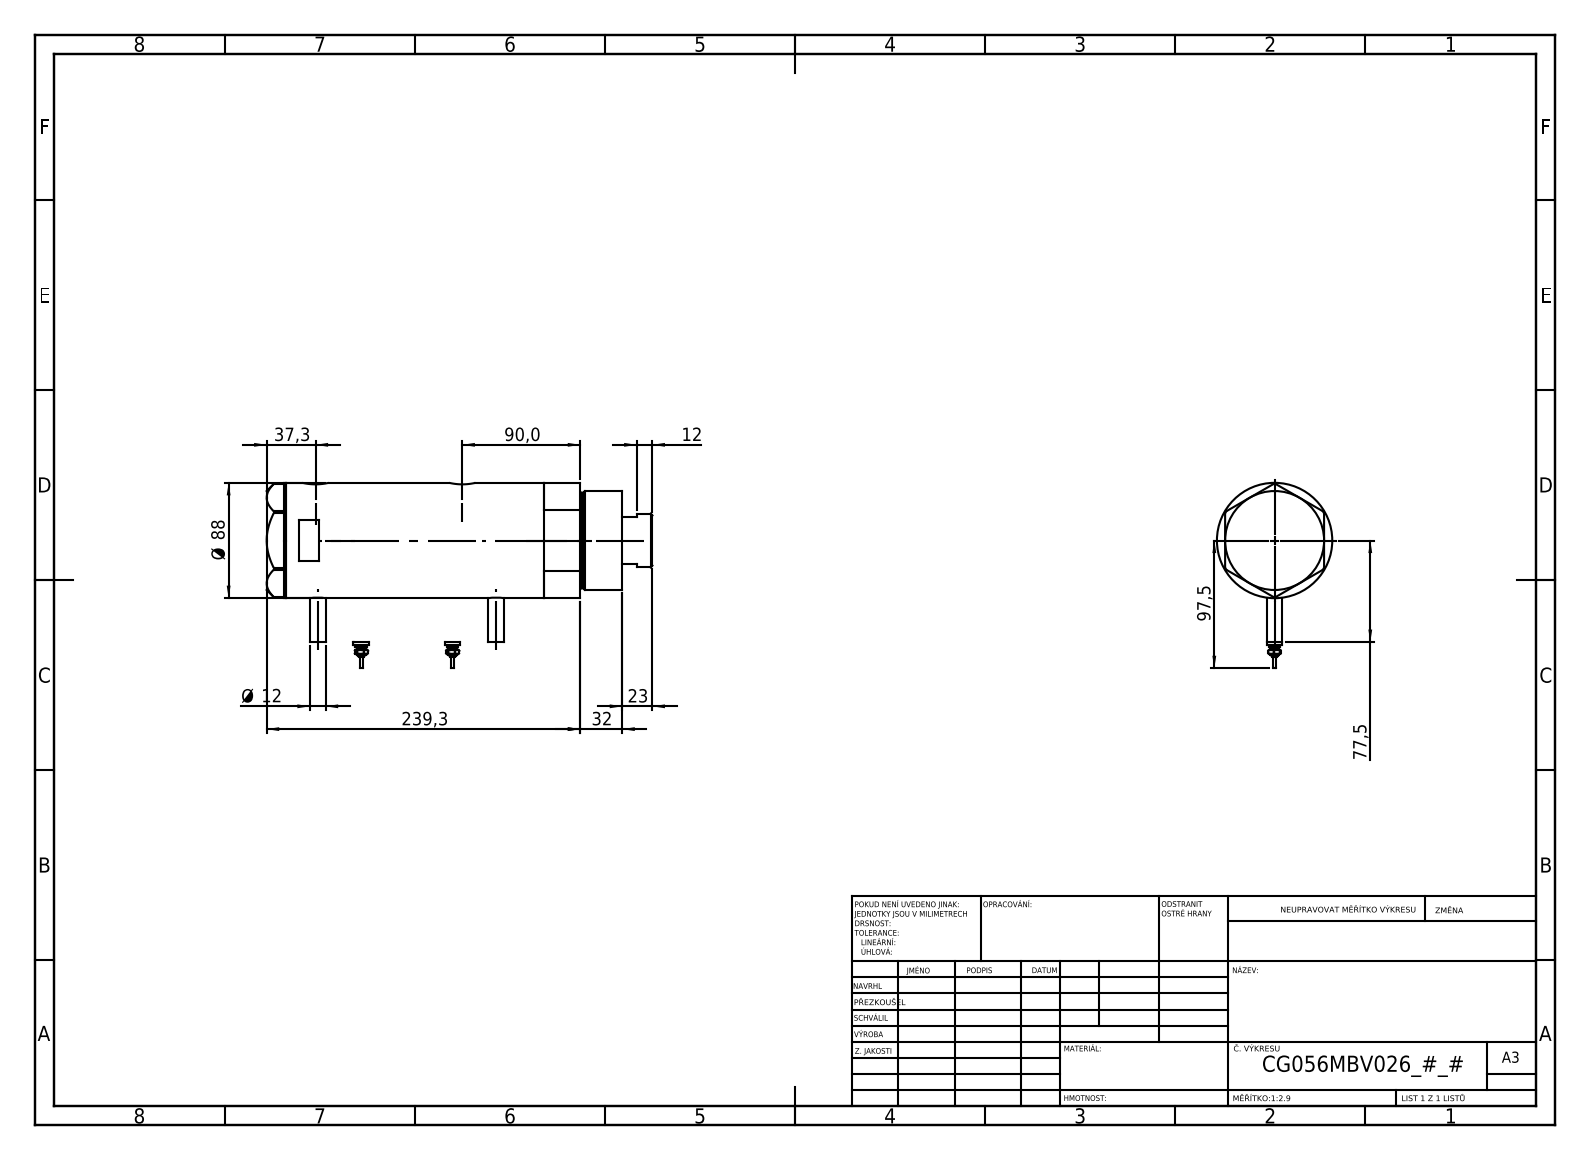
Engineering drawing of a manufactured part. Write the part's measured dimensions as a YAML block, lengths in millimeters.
part_name: "V270CG_BACK; Switch; V270CG_MIDDLE; V270CG_FRONT (+1 more)"
step_written_by: "SolidWorks 2019 (CONFIG_CONTROL_DESIGN)"
units: millimeters
bodies: {solids: 6, faces: 213, planar: 80, cylindrical: 69, other: 64}
overall_size: [294.3, 141.5, 88]
volume: 1567000
surface_area: 225645
round_holes:
  - {diameter: 12.5, count: 2}
  - {diameter: 13.16, count: 2}
  - {diameter: 20, count: 2}
  - {diameter: 14.5, count: 1}
  - {diameter: 42, count: 1}
  - {diameter: 43.5, count: 1}
  - {diameter: 56, count: 1}
  - {diameter: 60, count: 1}
  - {diameter: 80, count: 1}
round_bosses_or_shafts:
  - {diameter: 12, count: 4}
  - {diameter: 9, count: 2}
  - {diameter: 7, count: 2}
  - {diameter: 4.5, count: 2}
  - {diameter: 2.5, count: 2}
  - {diameter: 88, count: 1}
  - {diameter: 75, count: 1}
  - {diameter: 73, count: 1}
face_to_face_distances: [26, 108.4, 134.4, 15, 41, 149.4, 256.3, 271.3, 230.3, 121.9]
hole_center_spacings: [1.7, 25.8, 110.3, 112, 136.1, 137.8]
